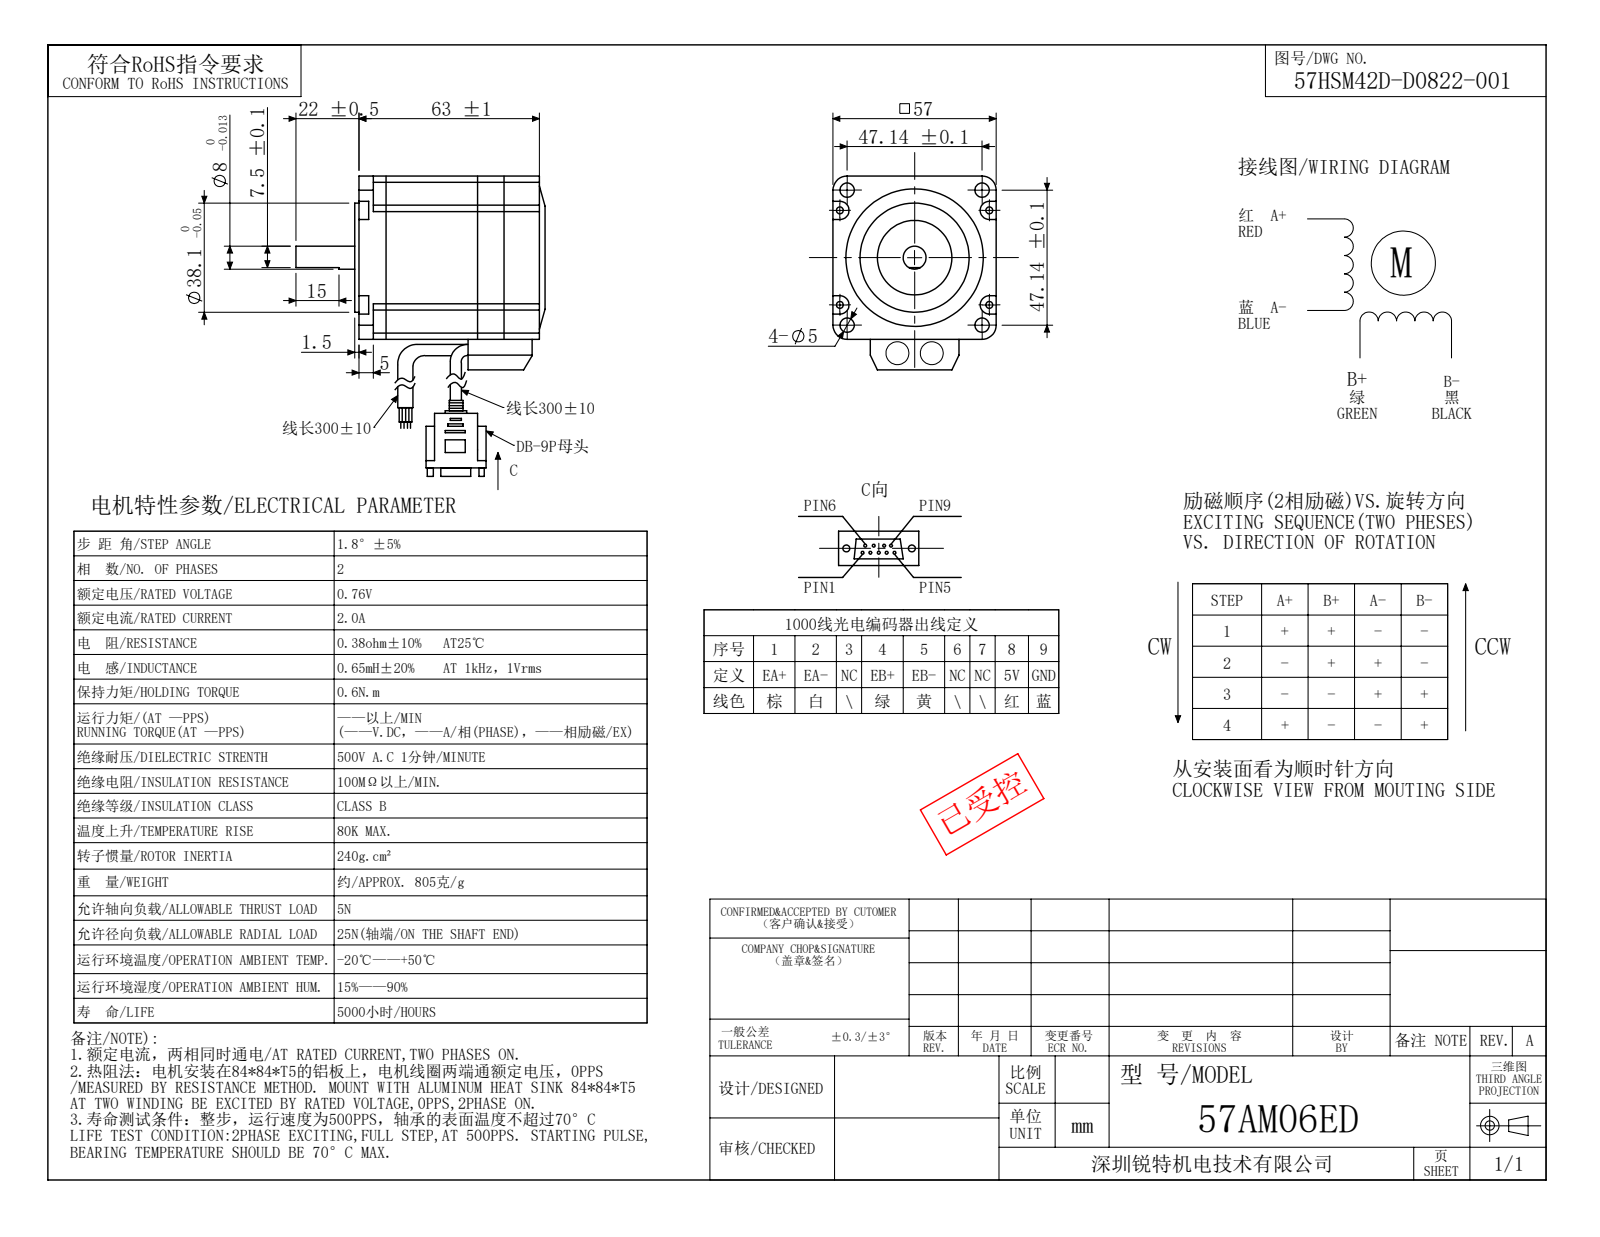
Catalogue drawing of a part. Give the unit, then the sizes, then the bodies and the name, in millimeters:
Units: millimetres
Overall size (bounding box): 87 × 67.7 × 57
Round holes (diameter × count): ⌀2.4 ×4, ⌀5 ×4, ⌀26 ×1, ⌀48 ×1
Round bosses / shafts (diameter × count): ⌀38.1 ×1, ⌀8 ×1
Partial cylindrical surfaces — rounded edges, fillets, slot ends (radius × count): R2.2 ×8, R3.2 ×4, R4.93 ×4, R8 ×4
Main face-to-face distances: 57, 65, 2, 63, 64.25, 62.25, 0.75, 66.5, 64.5, 2.25
Hole centre spacings: 7.51, 30.88, 33.33, 40.15, 47.14, 50.17, 63.82, 33
Volume: 192 735 mm³ · Surface area: 23 596 mm²
Bodies: 1 solid, 85 faces (37 planar, 46 cylindrical, 2 other)
Part name (STEP PRODUCT): 57HSM42D-D0822-001
STEP written by: SolidWorks 2020 (CONFIG_CONTROL_DESIGN)
